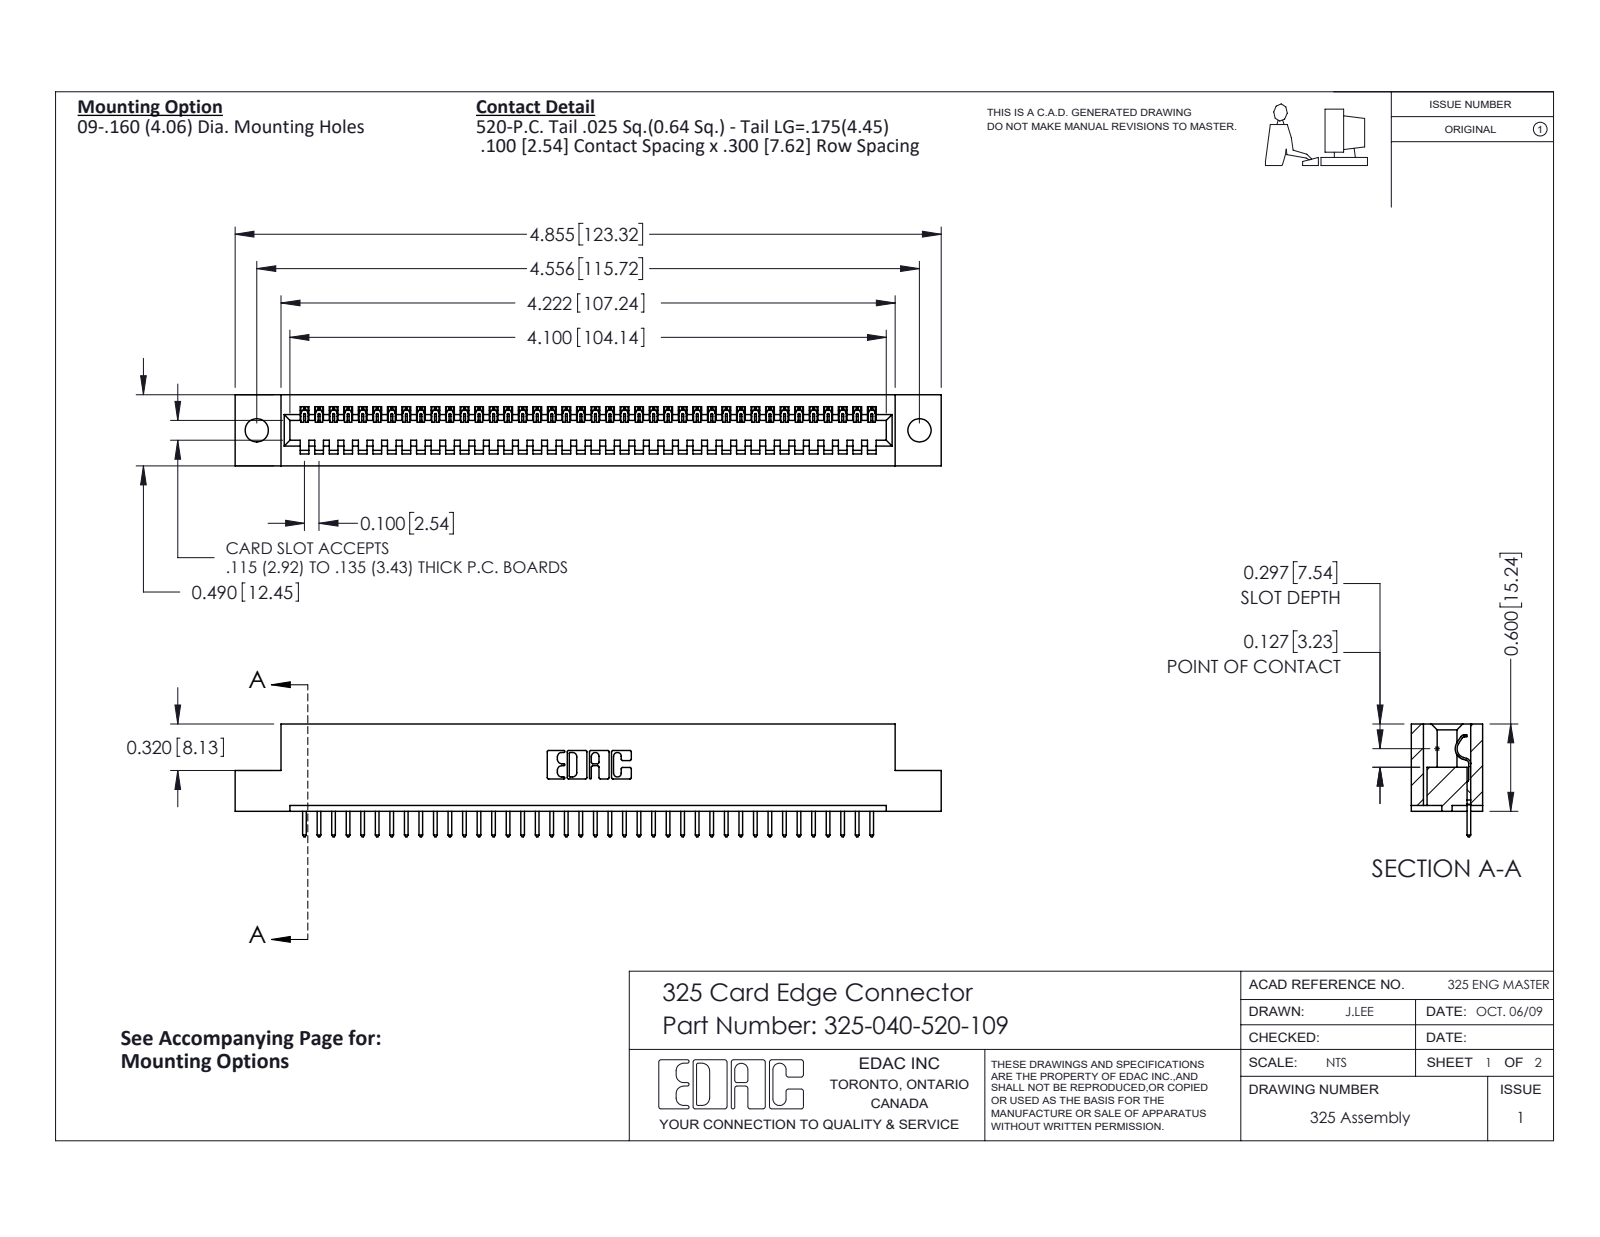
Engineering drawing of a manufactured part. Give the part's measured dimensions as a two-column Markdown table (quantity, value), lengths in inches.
| quantity | value |
| --- | --- |
| part name | 325 Part_.160 TH; 325-040-520-109; 325-292-001_325-293-120 |
| STEP written by | SolidWorks 2016 (CONFIG_CONTROL_DESIGN) |
| units | inches |
| bodies | 41 solids, 2434 faces (1750 planar, 684 cylindrical, 0 other) |
| overall size | 4.855 × 0.775 × 0.49 |
| volume | 0.934 in³ |
| surface area | 25.05 in² |
| round holes (diameter × count) | 0.16 × 2 |
| partial cylindrical surfaces (radius × count) | 0.006 × 80, 0.01 × 80, 0.01 × 22, 0.007 × 6, 0.031 × 6, 0.026 × 3, 0.014 × 1, 0.022 × 1 |
| main face-to-face distances | 0.083, 0.407, 0.49, 0.3, 0.107, 0.383, 0.025, 0.325, 0.56, 0.263 |
| hole center spacings | 4.556 |
